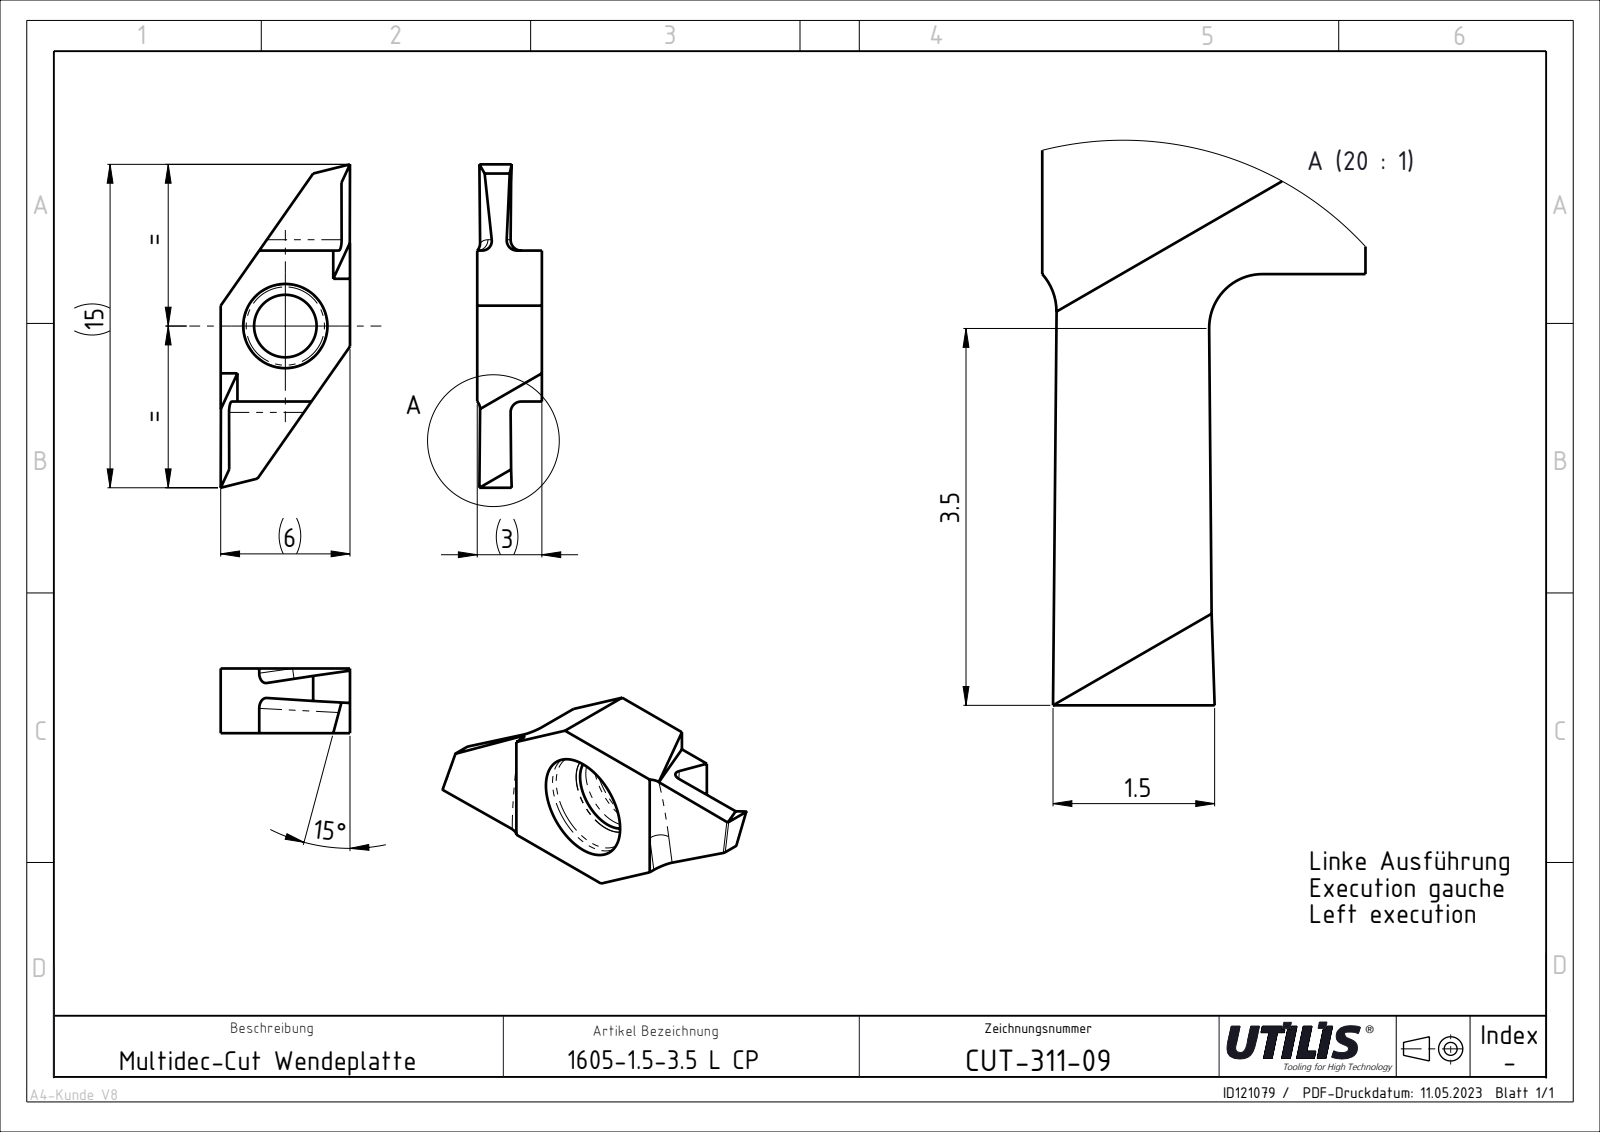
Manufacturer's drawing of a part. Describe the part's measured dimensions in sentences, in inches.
The part is named "CUT-311-09". Its 3-D file was written by "SolidWorks 2013 (CONFIG_CONTROL_DESIGN)". It is 1 solid with 28 faces: 14 planar, 6 cylindrical and 8 other. Overall it measures 0.591 by 0.236 by 0.118 inches. Its volume is 0.007 cubic inches and its surface area 0.338 square inches. Round holes: 1 of diameter 0.147. Partial cylindrical surfaces (rounded edges, fillets, slot ends): 4 of radius 0.02. The main face-to-face distances are 0.236, 0.118, 0.054, 0.157, 0.433, 0.276, 0.591.
